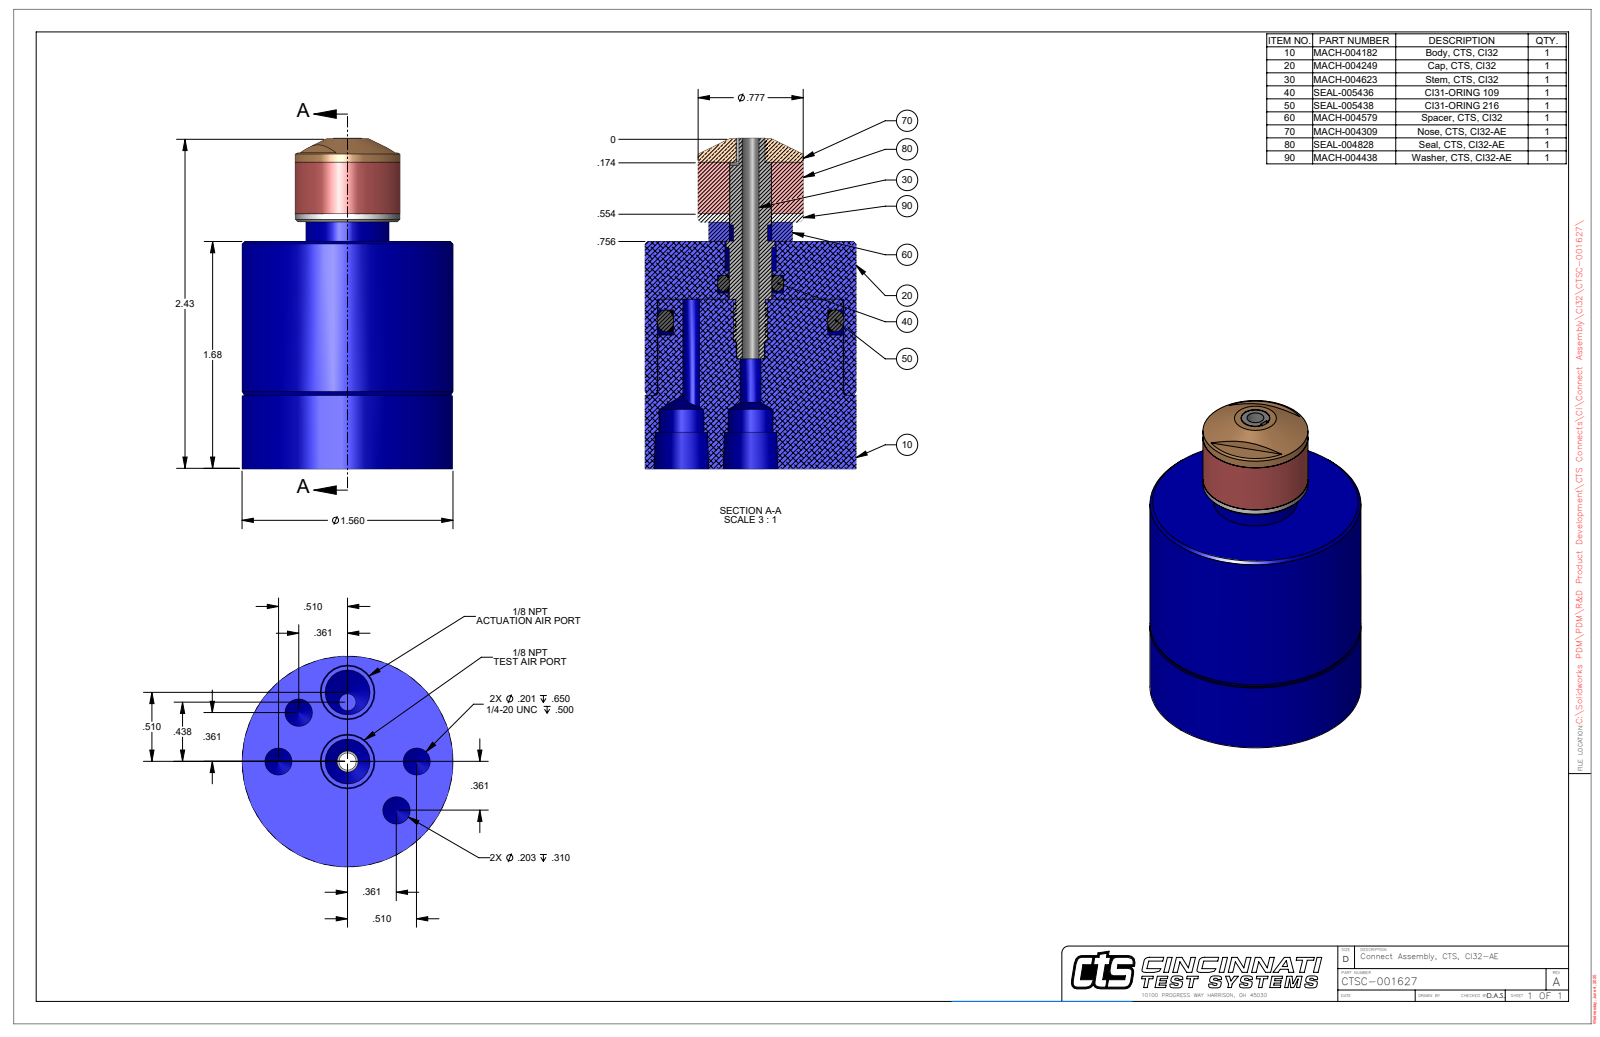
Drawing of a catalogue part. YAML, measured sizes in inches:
part_name: "CTSC-001627"
step_written_by: "SolidWorks 2023 (AUTOMOTIVE_DESIGN)"
units: inches
bodies: {solids: 1, faces: 102, planar: 29, cylindrical: 39, other: 34}
overall_size: [2.437, 1.56, 1.56]
volume: 3.304
surface_area: 20.05
round_holes:
  - {diameter: 0.125, count: 2}
  - {diameter: 0.201, count: 2}
  - {diameter: 0.203, count: 2}
  - {diameter: 0.332, count: 2}
  - {diameter: 0.156, count: 1}
  - {diameter: 0.314, count: 1}
  - {diameter: 0.38, count: 1}
  - {diameter: 1.377, count: 1}
round_bosses_or_shafts:
  - {diameter: 1.56, count: 1}
  - {diameter: 1.365, count: 1}
  - {diameter: 0.777, count: 1}
  - {diameter: 0.618, count: 1}
  - {diameter: 0.357, count: 1}
  - {diameter: 0.31, count: 1}
partial_cylinders:
  - {radius: 0.106, count: 1}
face_to_face_distances: [1.677, 1.819, 0.141, 0.542, 1.135, 1.276, 2.329, 1.787, 0.652, 0.51]
hole_center_spacings: [0.51, 0.39, 0.942, 0.672, 0.721, 0.072, 0.369, 0.437]
